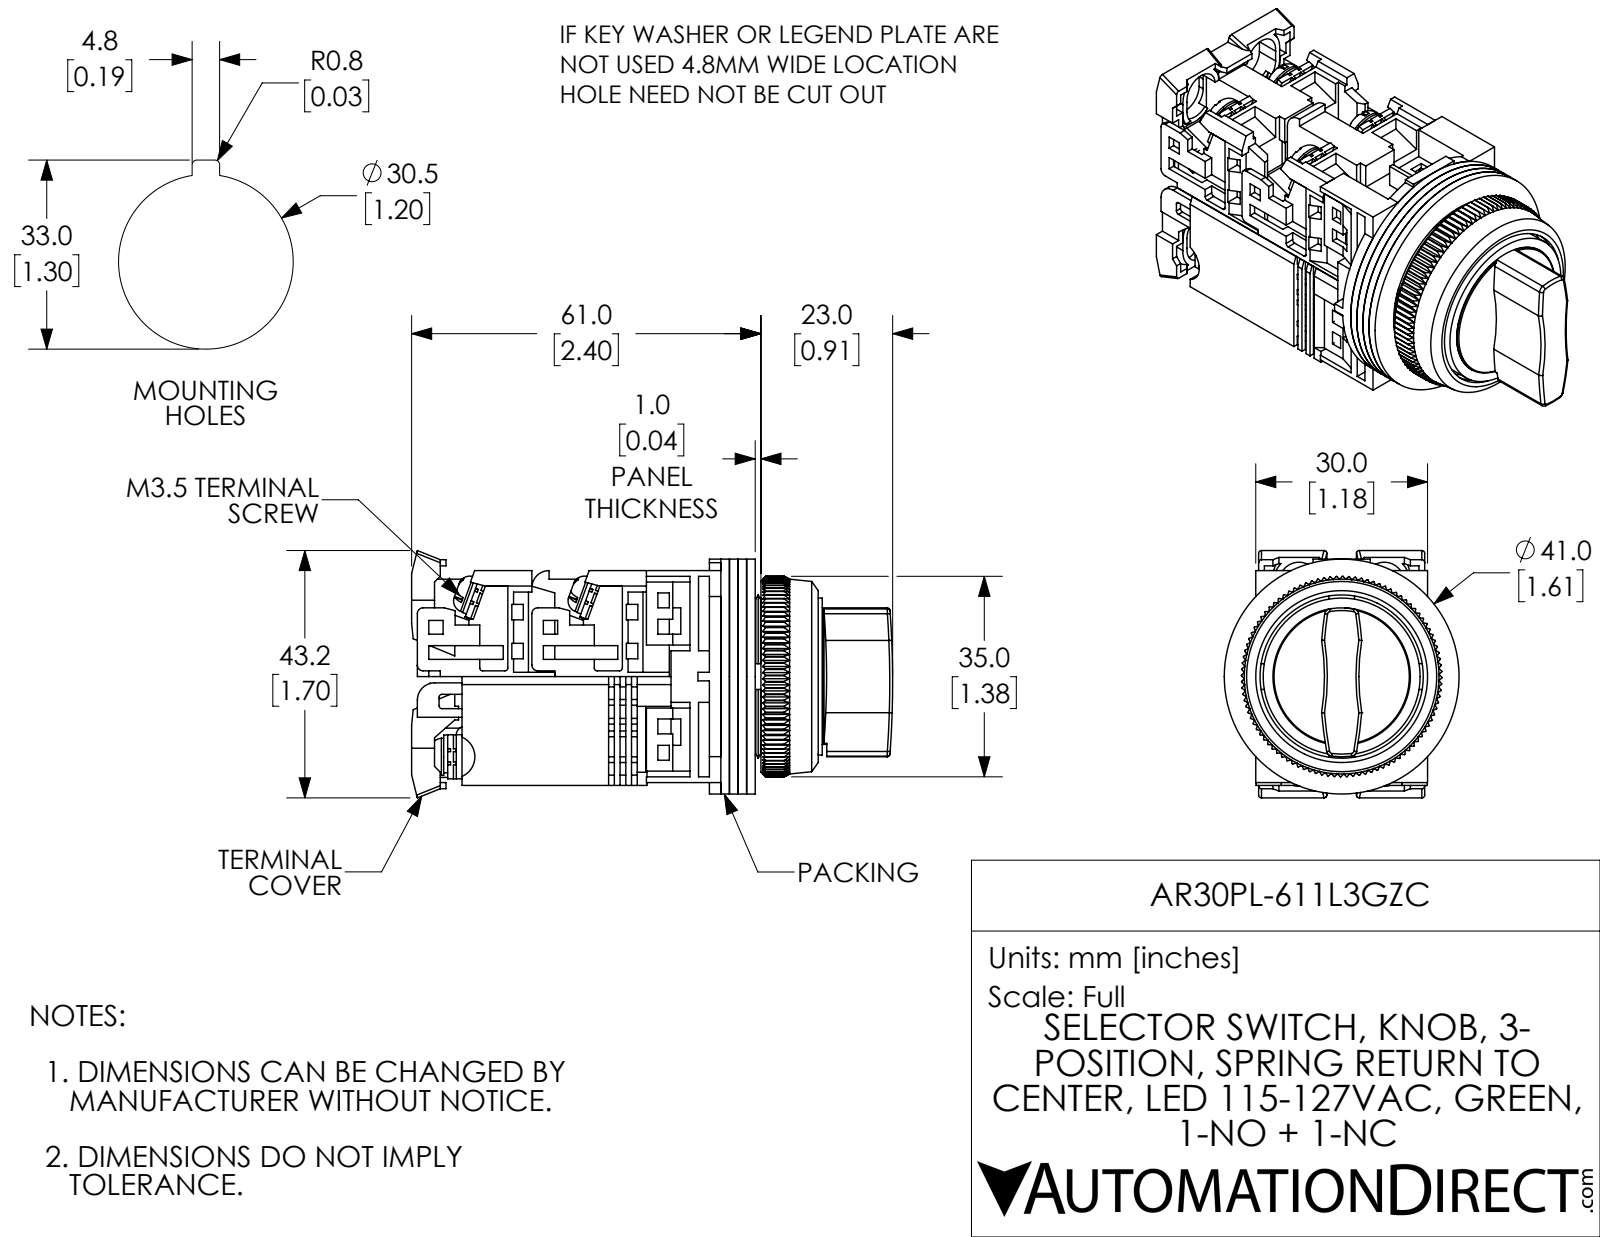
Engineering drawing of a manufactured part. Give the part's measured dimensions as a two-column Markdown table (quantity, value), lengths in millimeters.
| quantity | value |
| --- | --- |
| part name | AR30PL-611L3GZC |
| STEP written by | SolidWorks 2017 (AUTOMOTIVE_DESIGN) |
| units | millimeters |
| bodies | 34 solids, 2724 faces (2033 planar, 354 cylindrical, 337 other) |
| overall size | 84 × 43.2 × 41 |
| volume | 56 400 mm³ |
| surface area | 45 630 mm² |
| round holes (diameter × count) | 3.5 × 8, 3.6 × 6, 3 × 3, 12 × 1, 18 × 1, 19.5 × 1, 21 × 1, 28.5 × 1, 30 × 1, 31.8 × 1 |
| round bosses / shafts (diameter × count) | 6.6 × 6, 3.5 × 4, 1.6 × 2, 41 × 1, 29.2 × 1, 27.4 × 1, 24 × 1, 22.5 × 1 |
| partial cylindrical surfaces (radius × count) | 1.5 × 25, 0.5 × 15, 1 × 8, 3.5 × 4, 4.5 × 4, 3 × 3, 40 × 2, 75 × 2 |
| main face-to-face distances | 1.5, 3, 4.5, 1, 19, 2, 20, 1.6, 17.5, 5 |
| hole center spacings | 14.7, 6.8, 16.2, 7.5, 15.8, 0.5, 7.7, 14.8 |
